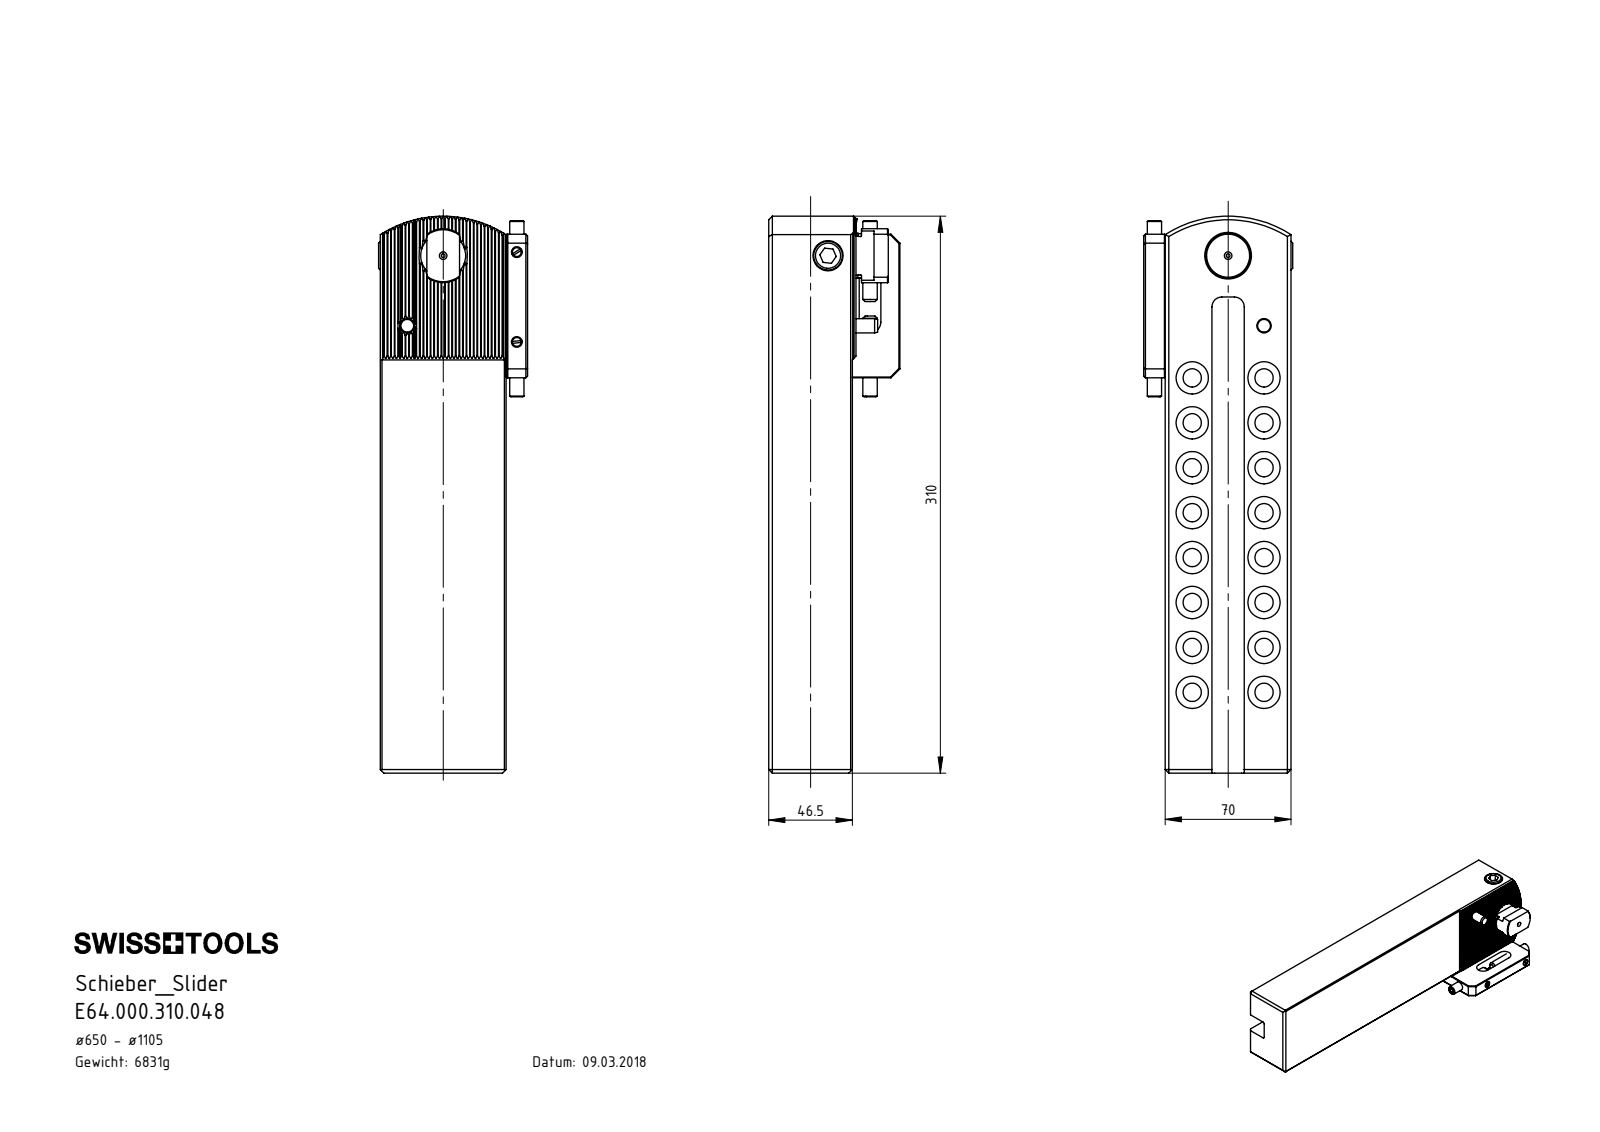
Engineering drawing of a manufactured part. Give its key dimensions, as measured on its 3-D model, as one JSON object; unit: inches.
{"part_name": "VK1-ER2.201.010_A_vorgespannt; ISO 8734 - 6 x 12; DIN 7984 - M10 x 16; VK1-ER7.001.012_B (+8 more)", "step_written_by": "SolidWorks 2017 (CONFIG_CONTROL_DESIGN)", "units": "inches", "bodies": {"solids": 13, "faces": 695, "planar": 311, "cylindrical": 239, "other": 145}, "overall_size": [12.205, 3.287, 2.874], "volume_in3": 53.14, "surface_area_in2": 223.2, "round_holes": [[0.709, 17], [0.402, 16], [0.197, 2], [0.236, 2], [0.268, 2], [0.079, 1], [0.315, 1], [0.335, 1], [0.413, 1], [0.433, 1], [0.551, 1], [0.984, 1]], "round_bosses_or_shafts": [[0.63, 2], [0.236, 2], [0.394, 1]], "partial_cylinders_radius": [[0.006, 33], [0.079, 4], [0.059, 3], [0.217, 2], [0.236, 2], [0.484, 1], [0.591, 1], [2.559, 1]], "face_to_face_distances": [2.756, 1.831, 1.732, 1.024, 1.043, 0.709, 0.787, 0.472, 1.496, 2.205], "hole_center_spacings": [0.984, 1.857, 1.969, 2.521, 2.953, 3.346, 1.575, 3.937]}
